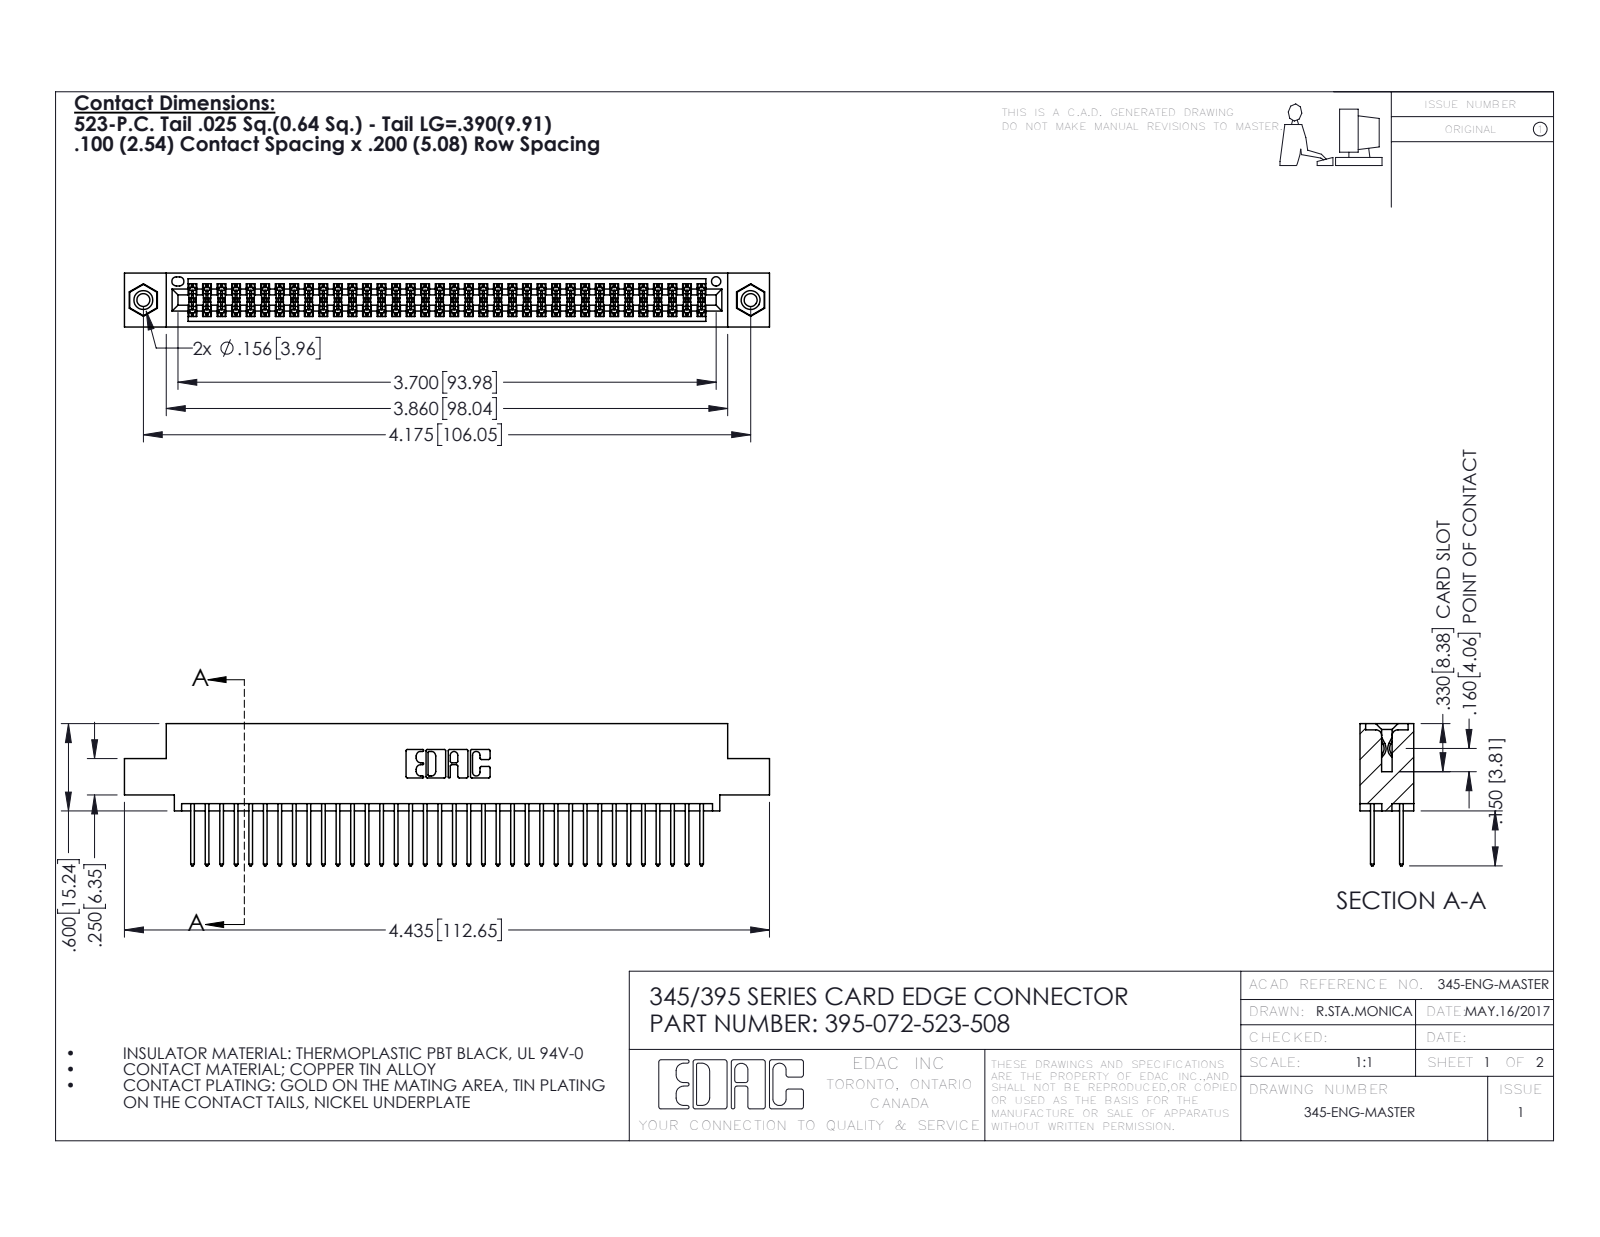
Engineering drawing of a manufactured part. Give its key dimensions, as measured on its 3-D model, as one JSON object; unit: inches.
{"part_name": "395-072-523-508; 345-292-001_345-293-123; 345-250-001_345-250-003-102; 345 Part_0.110 Offset - 0.156 Dia-TI", "step_written_by": "SolidWorks 2016 (CONFIG_CONTROL_DESIGN)", "units": "inches", "bodies": {"solids": 75, "faces": 3790, "planar": 2492, "cylindrical": 1282, "other": 16}, "overall_size": [4.435, 0.977, 0.37], "volume_in3": 0.669, "surface_area_in2": 26.11, "round_holes": [[0.089, 2], [0.125, 2], [0.156, 2], [0.064, 1]], "round_bosses_or_shafts": [[0.155, 2]], "partial_cylinders_radius": [[0.006, 108], [0.01, 72], [0.01, 22], [0.007, 6], [0.031, 6], [0.026, 3], [0.014, 2], [0.019, 2]], "face_to_face_distances": [0.072, 0.298, 0.2, 0.098, 0.272, 0.025, 0.37, 0.225, 0.175, 0.149], "hole_center_spacings": [0.27, 3.939, 4.175]}
